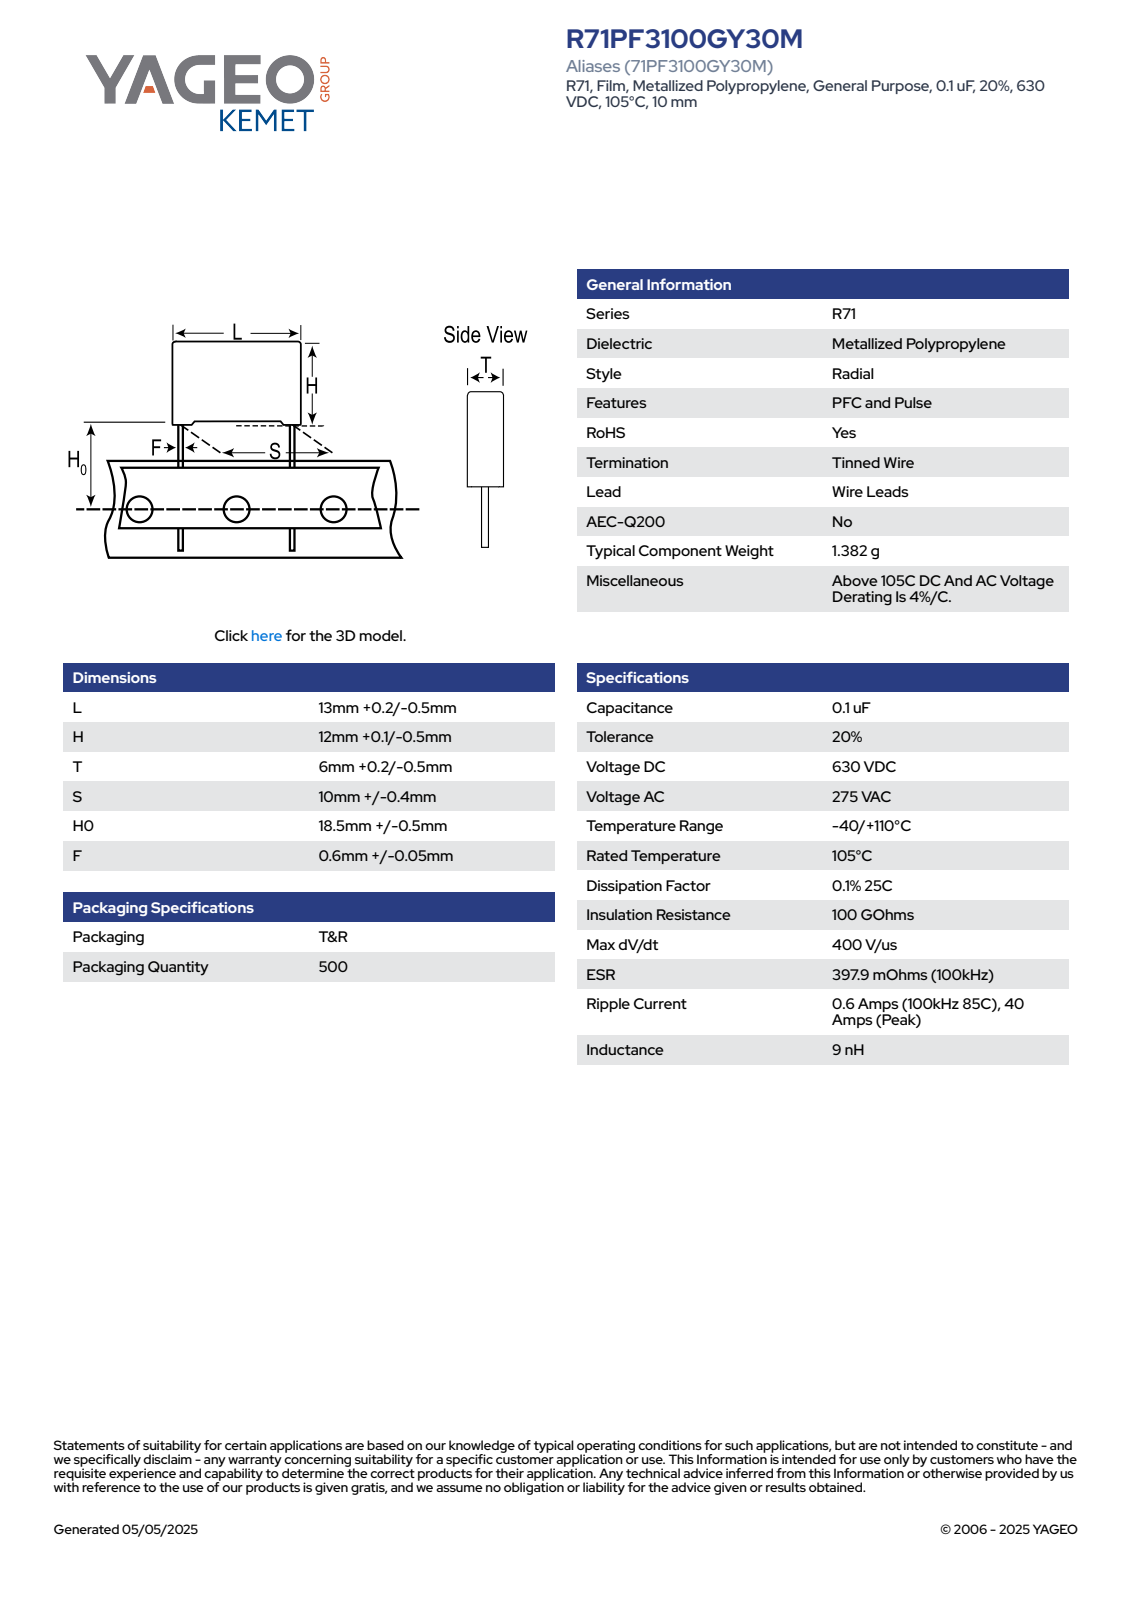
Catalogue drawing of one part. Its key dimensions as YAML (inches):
part_name: "CFR_RB2_13X12X6_L13.2H12.1T6.2S10H019F0.65"
step_written_by: "SolidWorks 2020 (AUTOMOTIVE_DESIGN)"
units: inches
bodies: {solids: 4, faces: 85, planar: 77, cylindrical: 8, other: 0}
overall_size: [1.224, 0.52, 0.244]
volume: 0.058
surface_area: 1.14
round_bosses_or_shafts:
  - {diameter: 0.026, count: 2}
partial_cylinders:
  - {radius: 0.02, count: 4}
face_to_face_distances: [0.244, 0.52, 0.447, 0.017, 0.227, 0.03, 0.476, 0.502, 0.209, 0.017]
